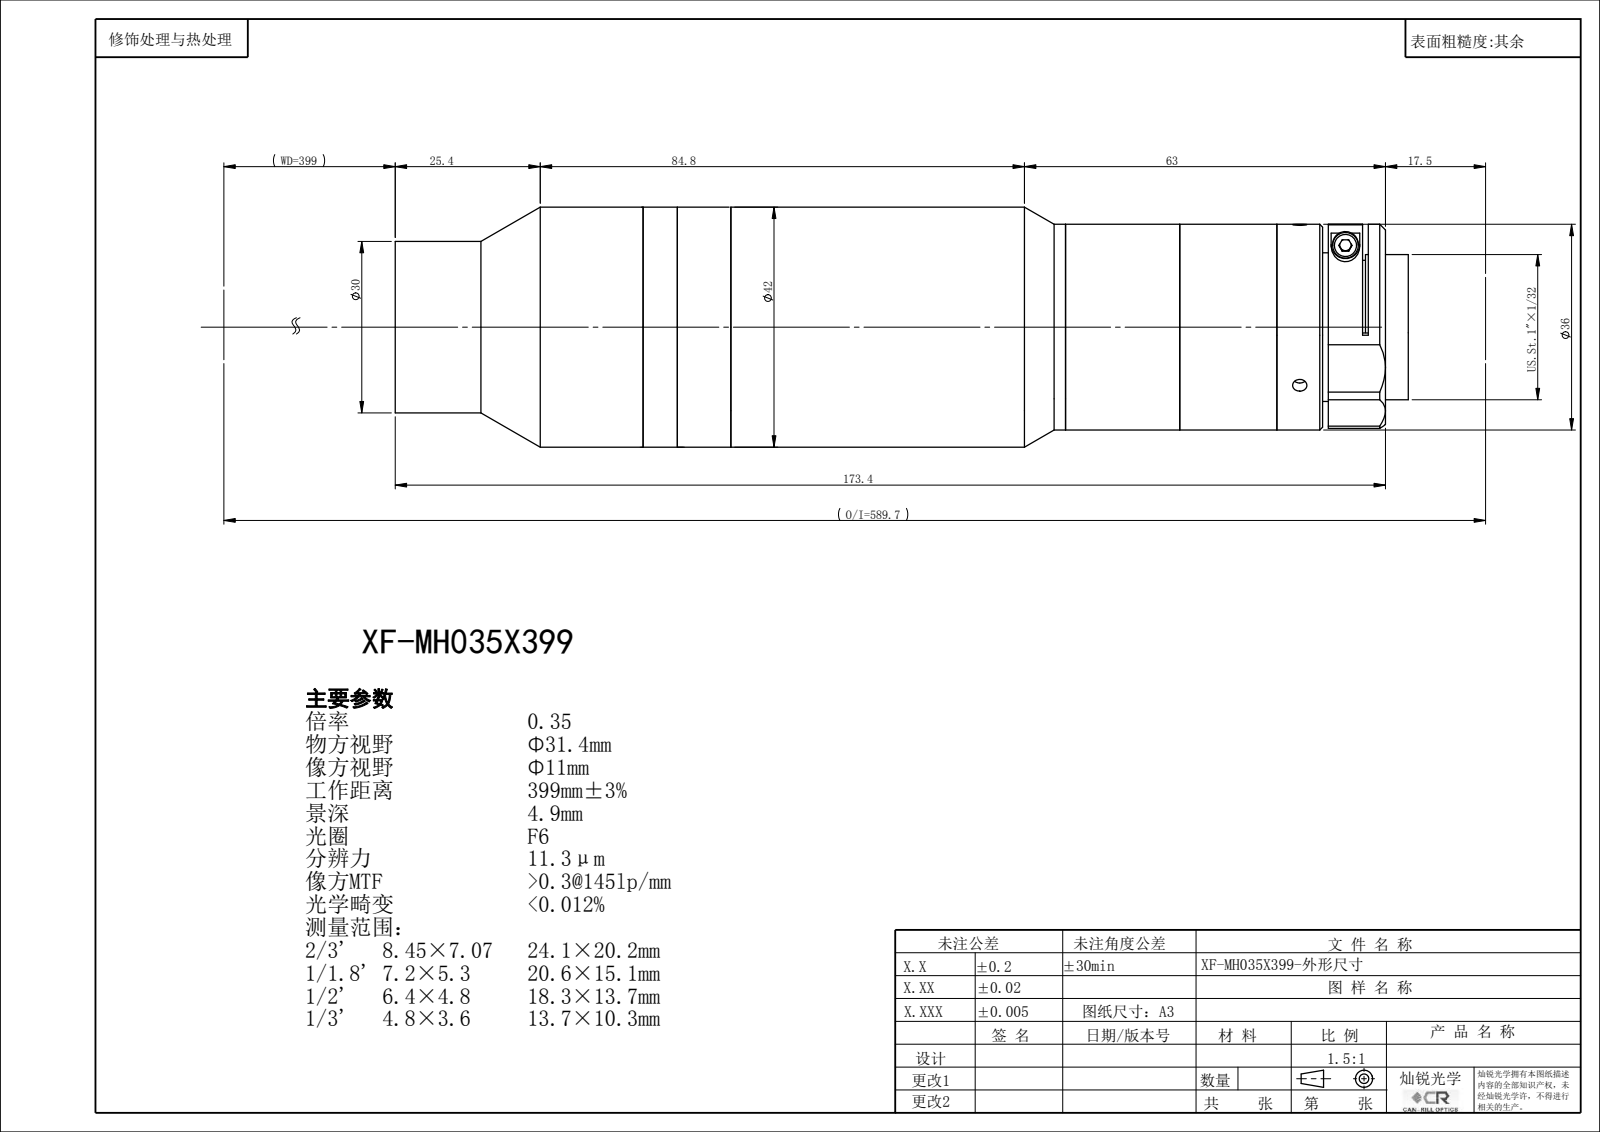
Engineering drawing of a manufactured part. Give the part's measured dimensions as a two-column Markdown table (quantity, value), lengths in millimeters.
| quantity | value |
| --- | --- |
| part name | XF-MH035X399 |
| STEP written by | SolidWorks 2022 (CONFIG_CONTROL_DESIGN) |
| units | millimeters |
| bodies | 0 solids, 137 faces (69 planar, 44 cylindrical, 24 other) |
| overall size | 177.11 × 42 × 42 |
| round holes (diameter × count) | 2.5 × 3, 22.4 × 1, 24 × 1, 26.4 × 1 |
| round bosses / shafts (diameter × count) | 42 × 1, 36 × 1, 34 × 1, 30 × 1, 25.4 × 1 |
| main face-to-face distances | 18.76, 1.5, 17.26, 6, 17, 34.26, 35.76, 20, 37, 54.26 |
